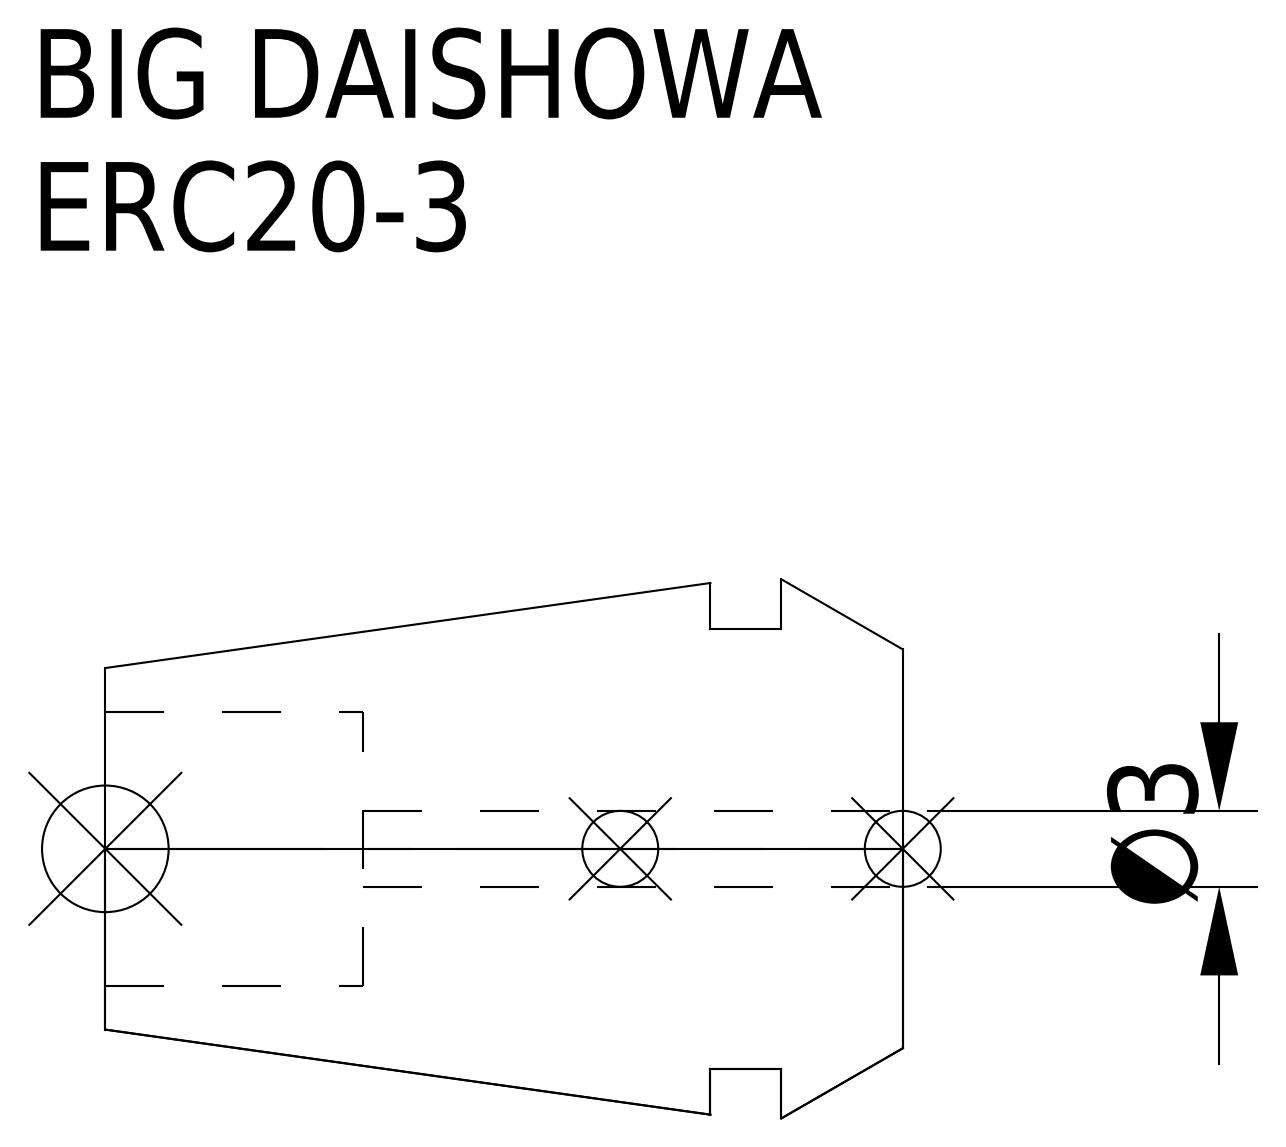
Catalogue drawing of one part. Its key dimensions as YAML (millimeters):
part_name: "ERC20-3"
step_written_by: "CREO PARAMETRIC BY PTC INC, 2016380 (AUTOMOTIVE_DESIGN)"
units: millimeters
bodies: {solids: 1, faces: 15, planar: 5, cylindrical: 6, other: 4}
overall_size: [31.5, 21.3, 21.3]
volume: 6798
surface_area: 2928
round_holes:
  - {diameter: 3, count: 1}
  - {diameter: 10.8, count: 1}
round_bosses_or_shafts:
  - {diameter: 17.4, count: 1}
face_to_face_distances: [4.8, 7.6, 2.8, 21.31, 16.51, 13.71, 31.5, 26.7, 23.9, 10.19]
